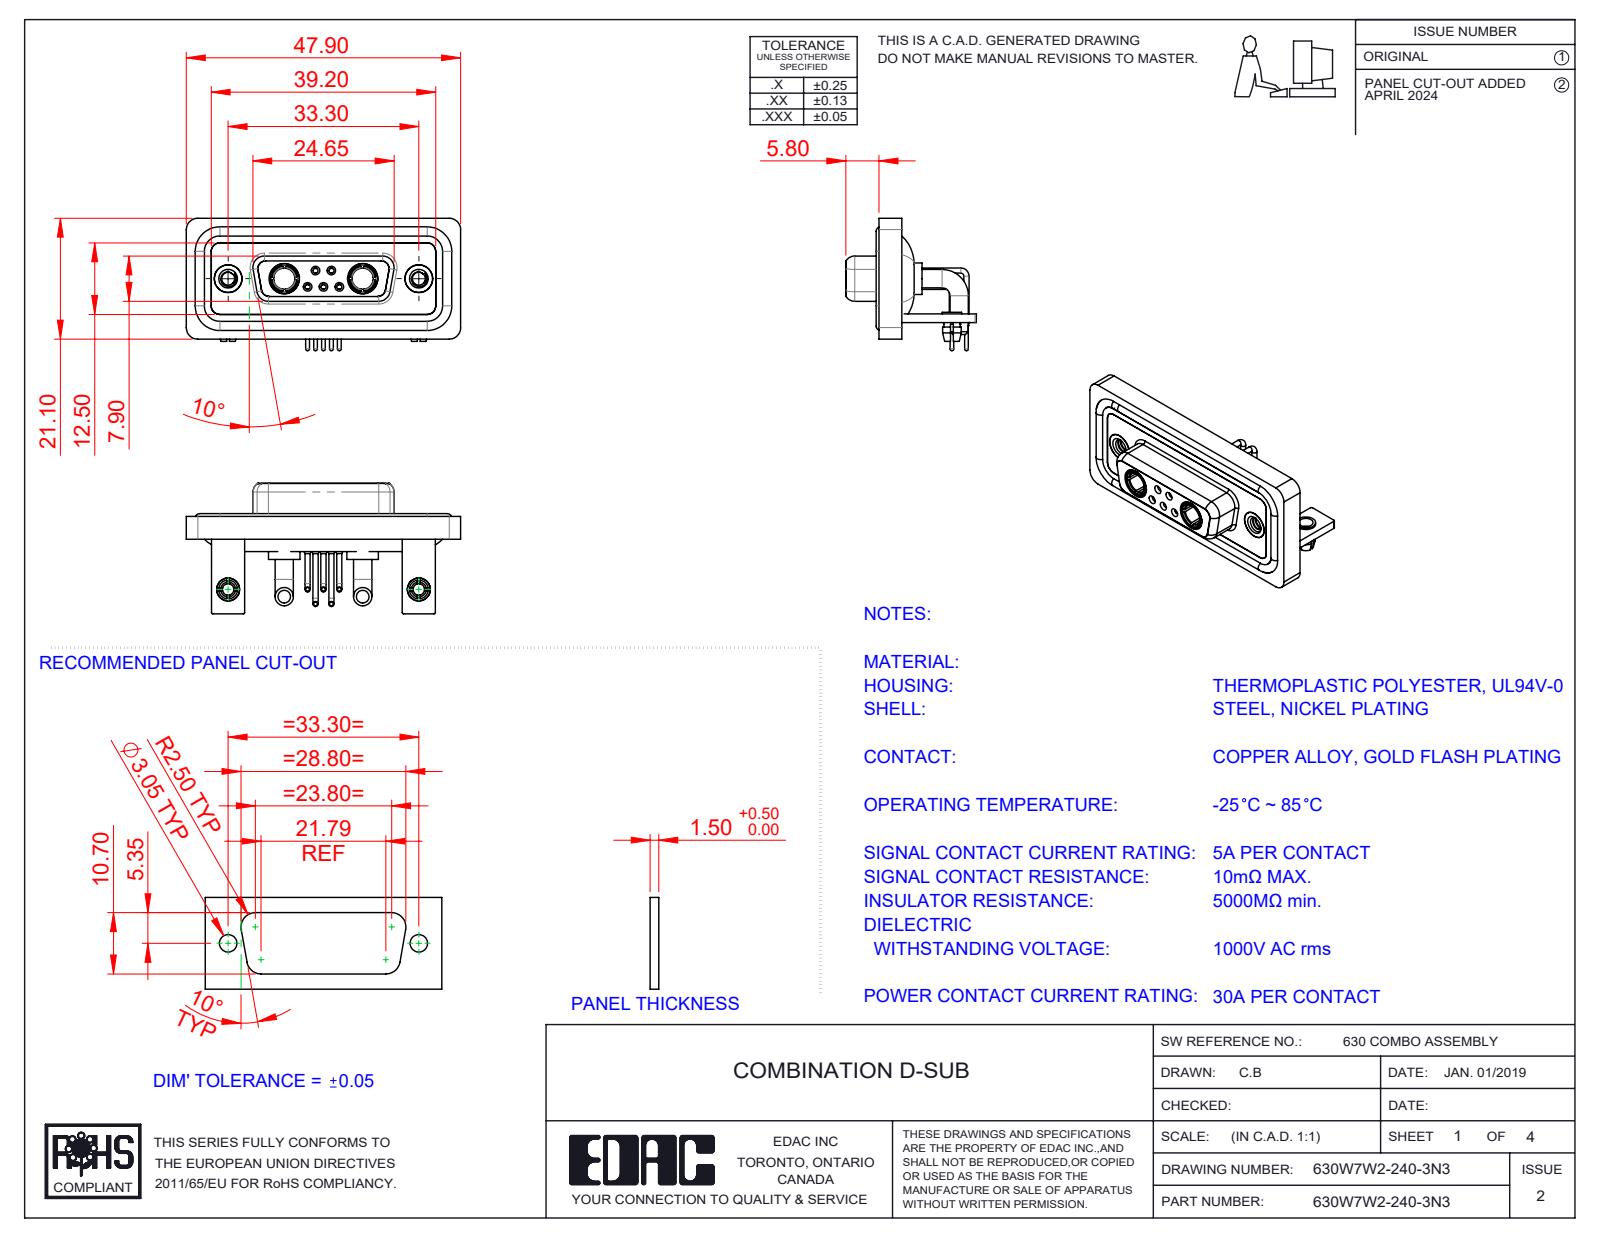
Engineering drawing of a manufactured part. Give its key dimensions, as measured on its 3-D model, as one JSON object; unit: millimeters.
{"part_name": "630Combo Shell Front_15 Contacts; 630Combo Shell Rear_15 Contacts; 630Combo Contact Row 1_50 Contacts; Power Socket_30A RA (+7 more)", "step_written_by": "SolidWorks 2023 (CONFIG_CONTROL_DESIGN)", "units": "millimeters", "bodies": {"solids": 20, "faces": 947, "planar": 306, "cylindrical": 409, "other": 232}, "overall_size": [47.9, 23.12, 22.8], "volume_mm3": 6655, "surface_area_mm2": 11188, "round_holes": [[2, 7], [0.9, 5], [1.1, 5], [1.5, 5], [4.85, 4], [1.6, 3], [1.7, 2], [2.26, 2], [2.5, 2], [3.2, 2], [3.7, 2], [4, 2]], "round_bosses_or_shafts": [[1.6, 6], [0.9, 5], [0.65, 5], [3.2, 4], [5.5, 2], [5.2, 2], [4.96, 2], [4.95, 2]], "partial_cylinders_radius": [[2, 21], [1.5, 18], [0.25, 16], [1.35, 12], [1.6, 8], [0.5, 5], [0.6, 4], [0.65, 4]], "face_to_face_distances": [0.4, 2.9, 1.5, 1.8, 3.7, 1.1, 4.1, 1.6, 2.5, 1.4], "hole_center_spacings": [3.16, 2.77, 9.8, 23.5, 33.3, 4.31, 4.33, 5.03]}
